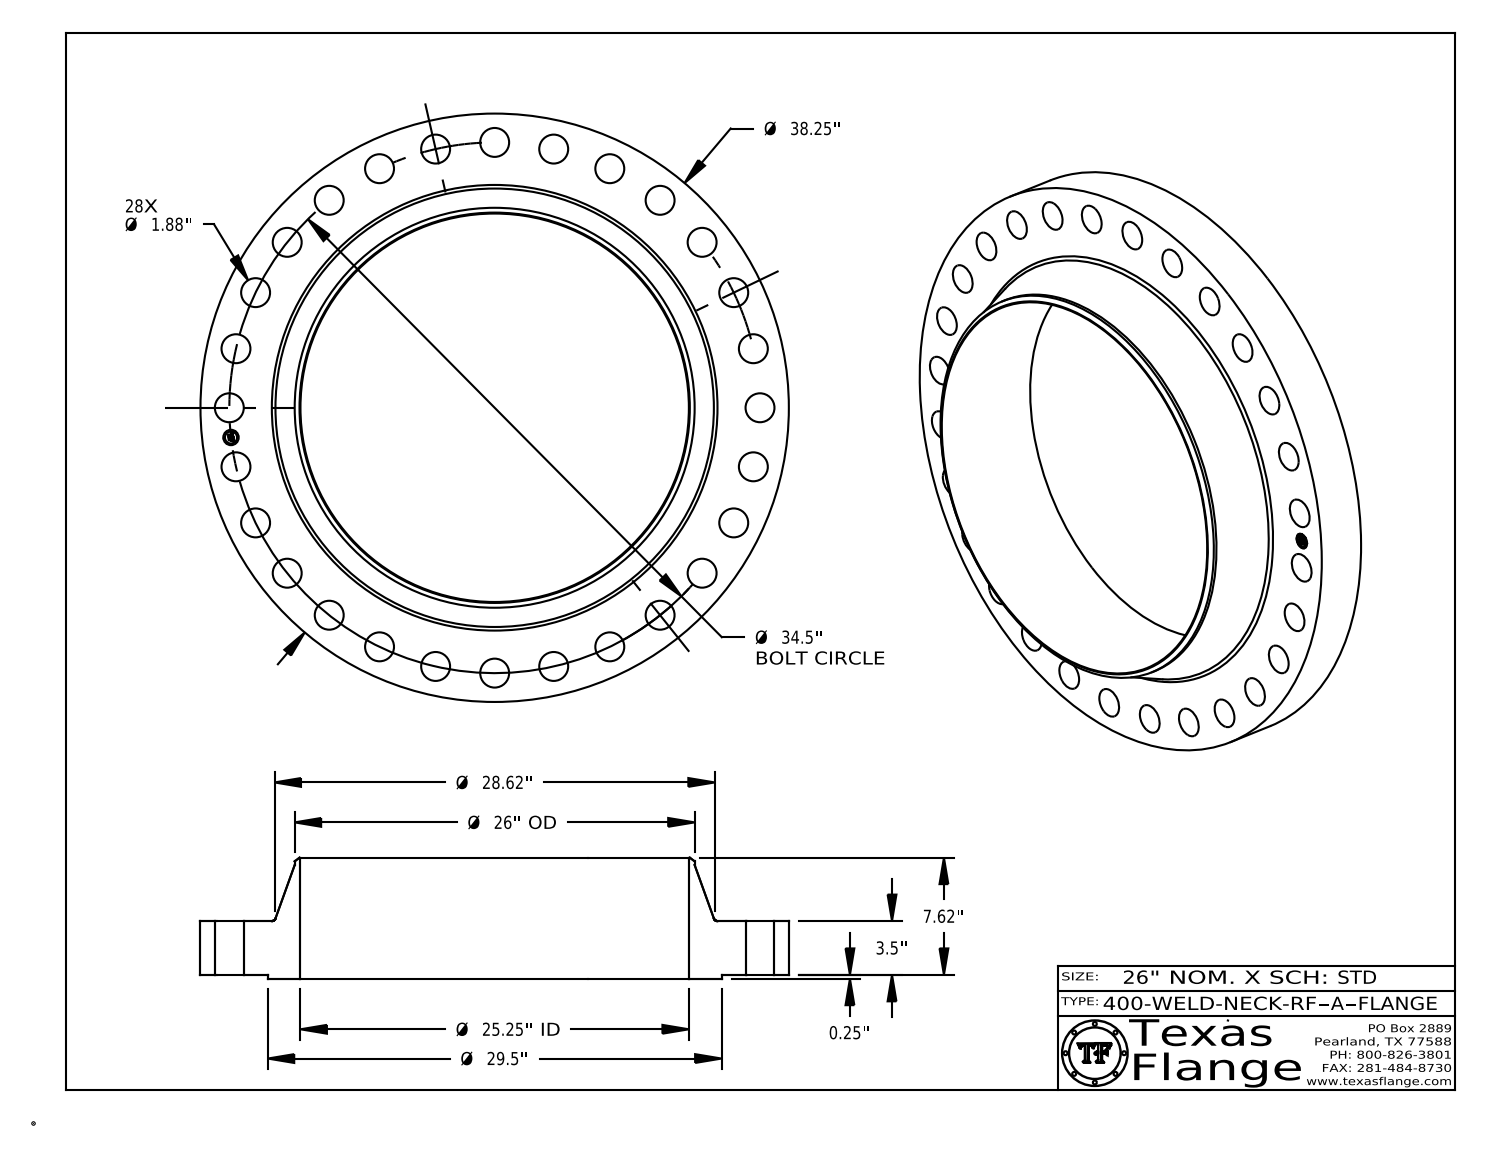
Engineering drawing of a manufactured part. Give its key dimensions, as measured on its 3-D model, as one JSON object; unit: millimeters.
{"part_name": "400-WELD-NECK-RF, Series A", "step_written_by": "CATIA V5 STEP AP214 (AUTOMOTIVE_DESIGN)", "units": "millimeters", "bodies": {"solids": 1, "faces": 459, "planar": 369, "cylindrical": 84, "other": 6}, "overall_size": [971.6, 971.6, 199.9], "volume_mm3": 38770000, "surface_area_mm2": 1955000, "round_holes": [[47.8, 28], [25.4, 1], [641.4, 1]], "round_bosses_or_shafts": [[1.5, 8], [971.6, 1], [749.3, 1], [660.4, 1], [20, 1]], "face_to_face_distances": [88.9, 6.4, 95.3, 199.9, 193.5, 104.6, 0.4, 94.9, 88.5, 105], "hole_center_spacings": [438.2, 685.1, 870.8, 380.2, 466.2, 827.1, 854.3, 289.4]}
